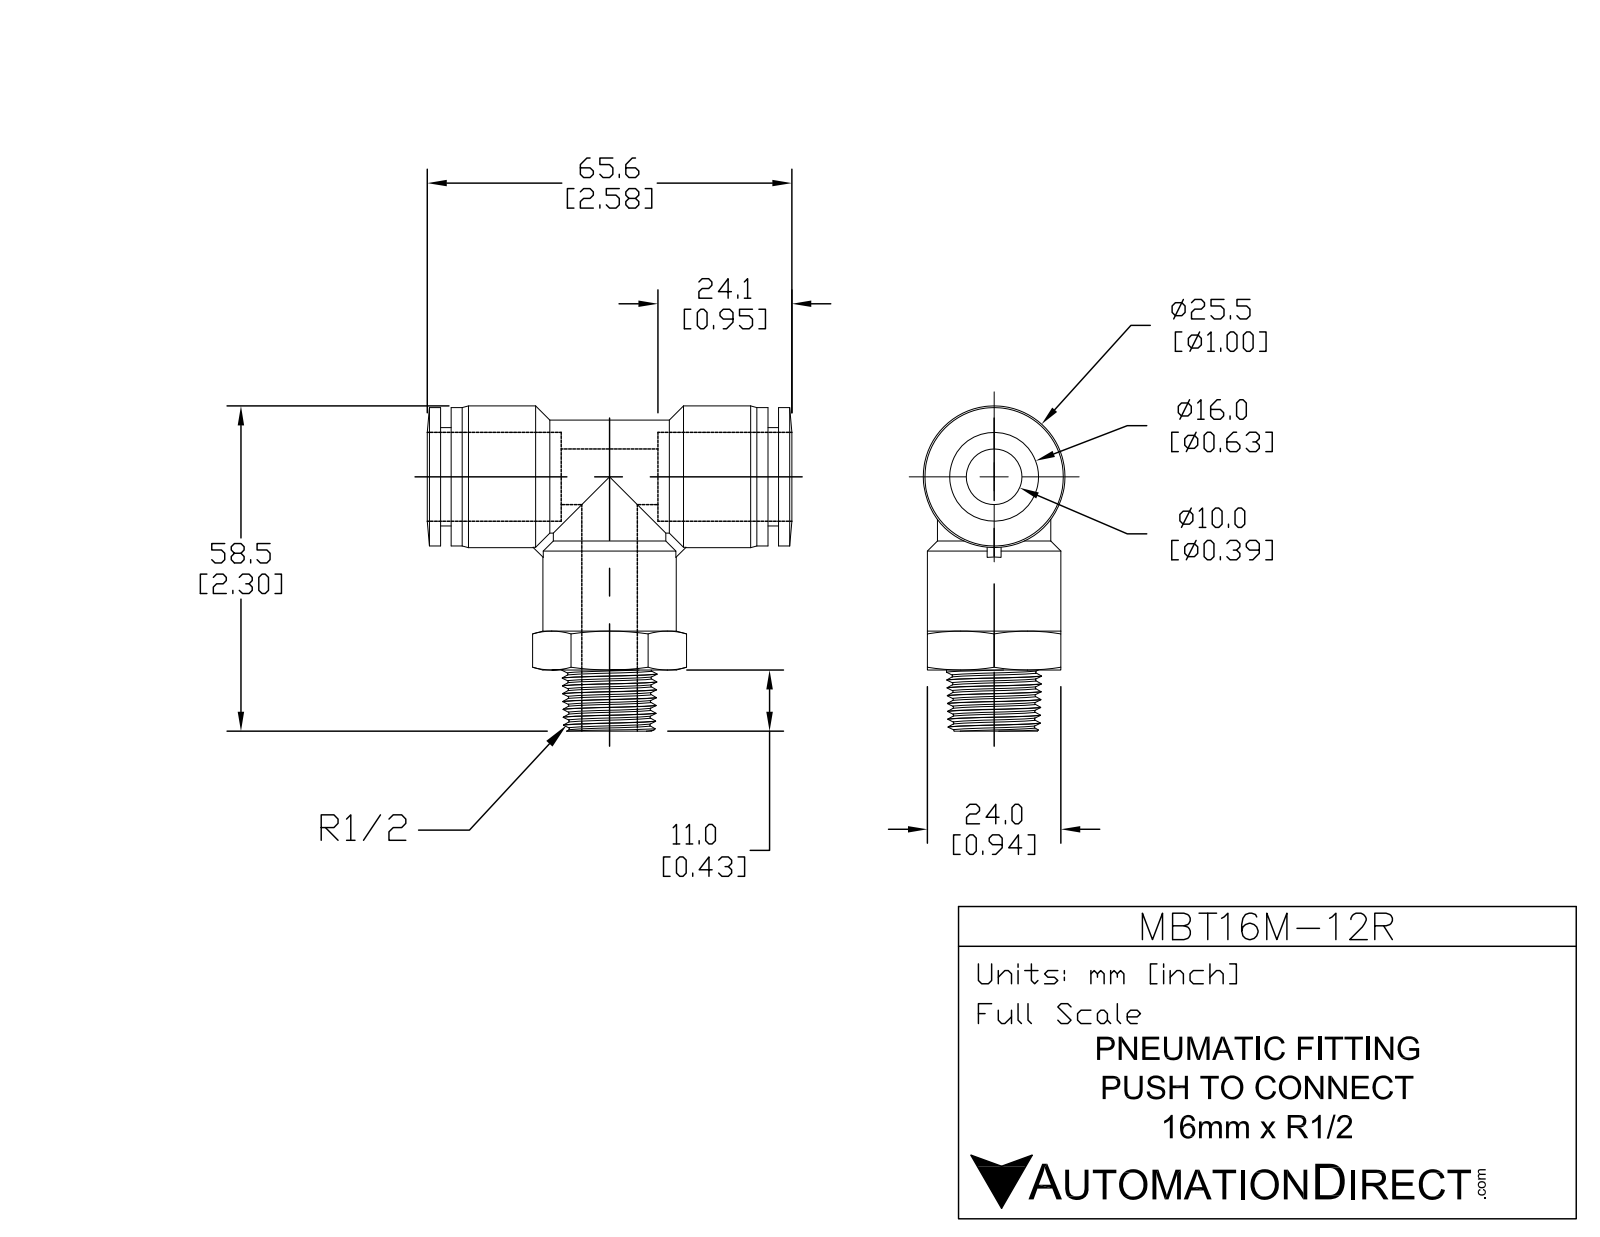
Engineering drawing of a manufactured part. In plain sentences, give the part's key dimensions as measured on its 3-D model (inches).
The part is named "MBT16M-12R". Its 3-D file was written by "SolidWorks 2015 (AUTOMOTIVE_DESIGN)". It is 1 solid with 95 faces: 20 planar, 31 cylindrical and 44 other. Overall it measures 2.583 by 2.305 by 1.004 inches. Its volume is 1.53 cubic inches and its surface area 21.51 square inches. Round holes: 2 of diameter 0.512, 1 of diameter 0.642. Round bosses or shafts: 2 of diameter 0.803, 1 of diameter 1.004, 1 of diameter 0.992, 1 of diameter 0.984, 1 of diameter 0.945, 1 of diameter 0.709. The main face-to-face distances are 0.945, 0.063, 2.299, 2.362, 0.839, 1.524, 0.776, 1.461, 2.236, 0.551.
